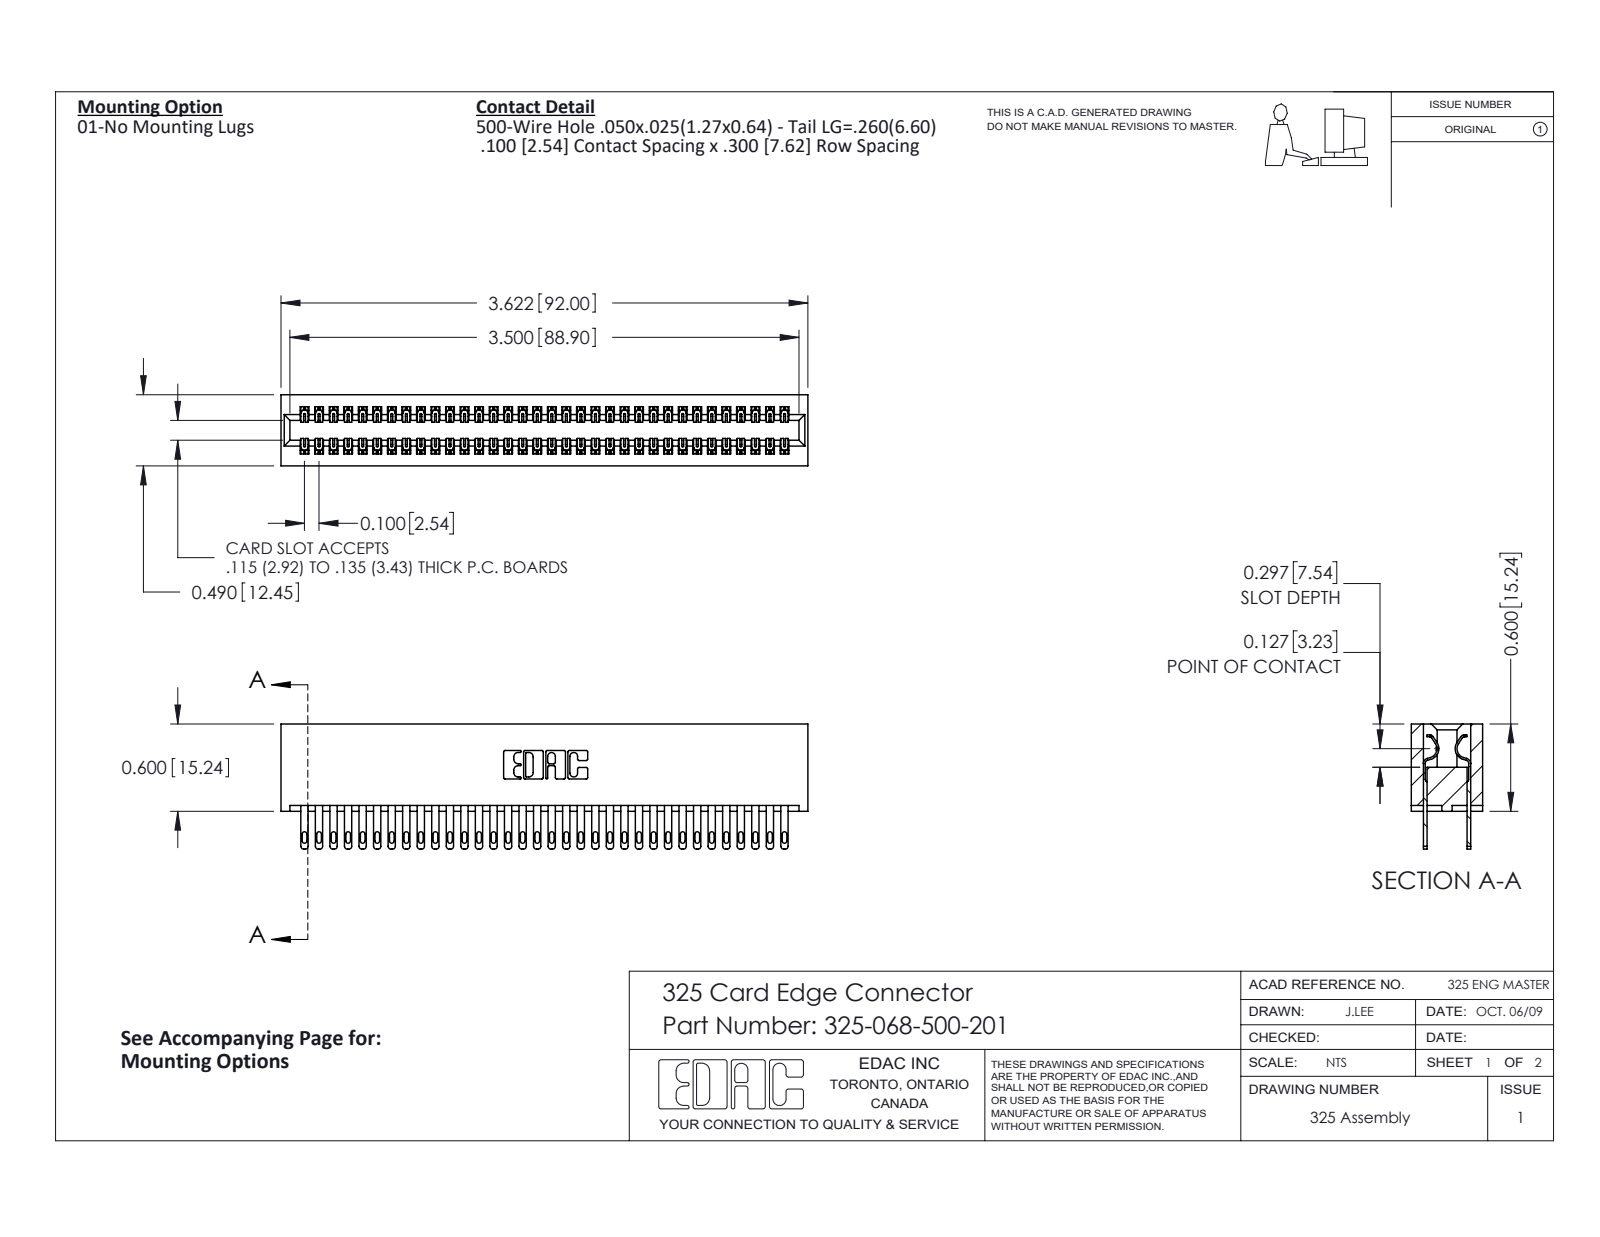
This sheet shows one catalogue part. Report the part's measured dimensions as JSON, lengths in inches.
{"part_name": "325-292-001_325-293-100; 325 Part_Lugless; 325-068-500-201", "step_written_by": "SolidWorks 2016 (CONFIG_CONTROL_DESIGN)", "units": "inches", "bodies": {"solids": 69, "faces": 3370, "planar": 2106, "cylindrical": 1264, "other": 0}, "overall_size": [3.622, 0.86, 0.49], "volume_in3": 0.77, "surface_area_in2": 25.51, "partial_cylinders_radius": [[0.006, 102], [0.016, 68], [0.02, 68], [0.01, 22], [0.007, 6], [0.031, 6], [0.026, 3], [0.014, 2]], "face_to_face_distances": [0.083, 0.407, 0.3, 0.107, 0.383, 0.025, 0.325, 0.49, 0.275, 0.1]}
